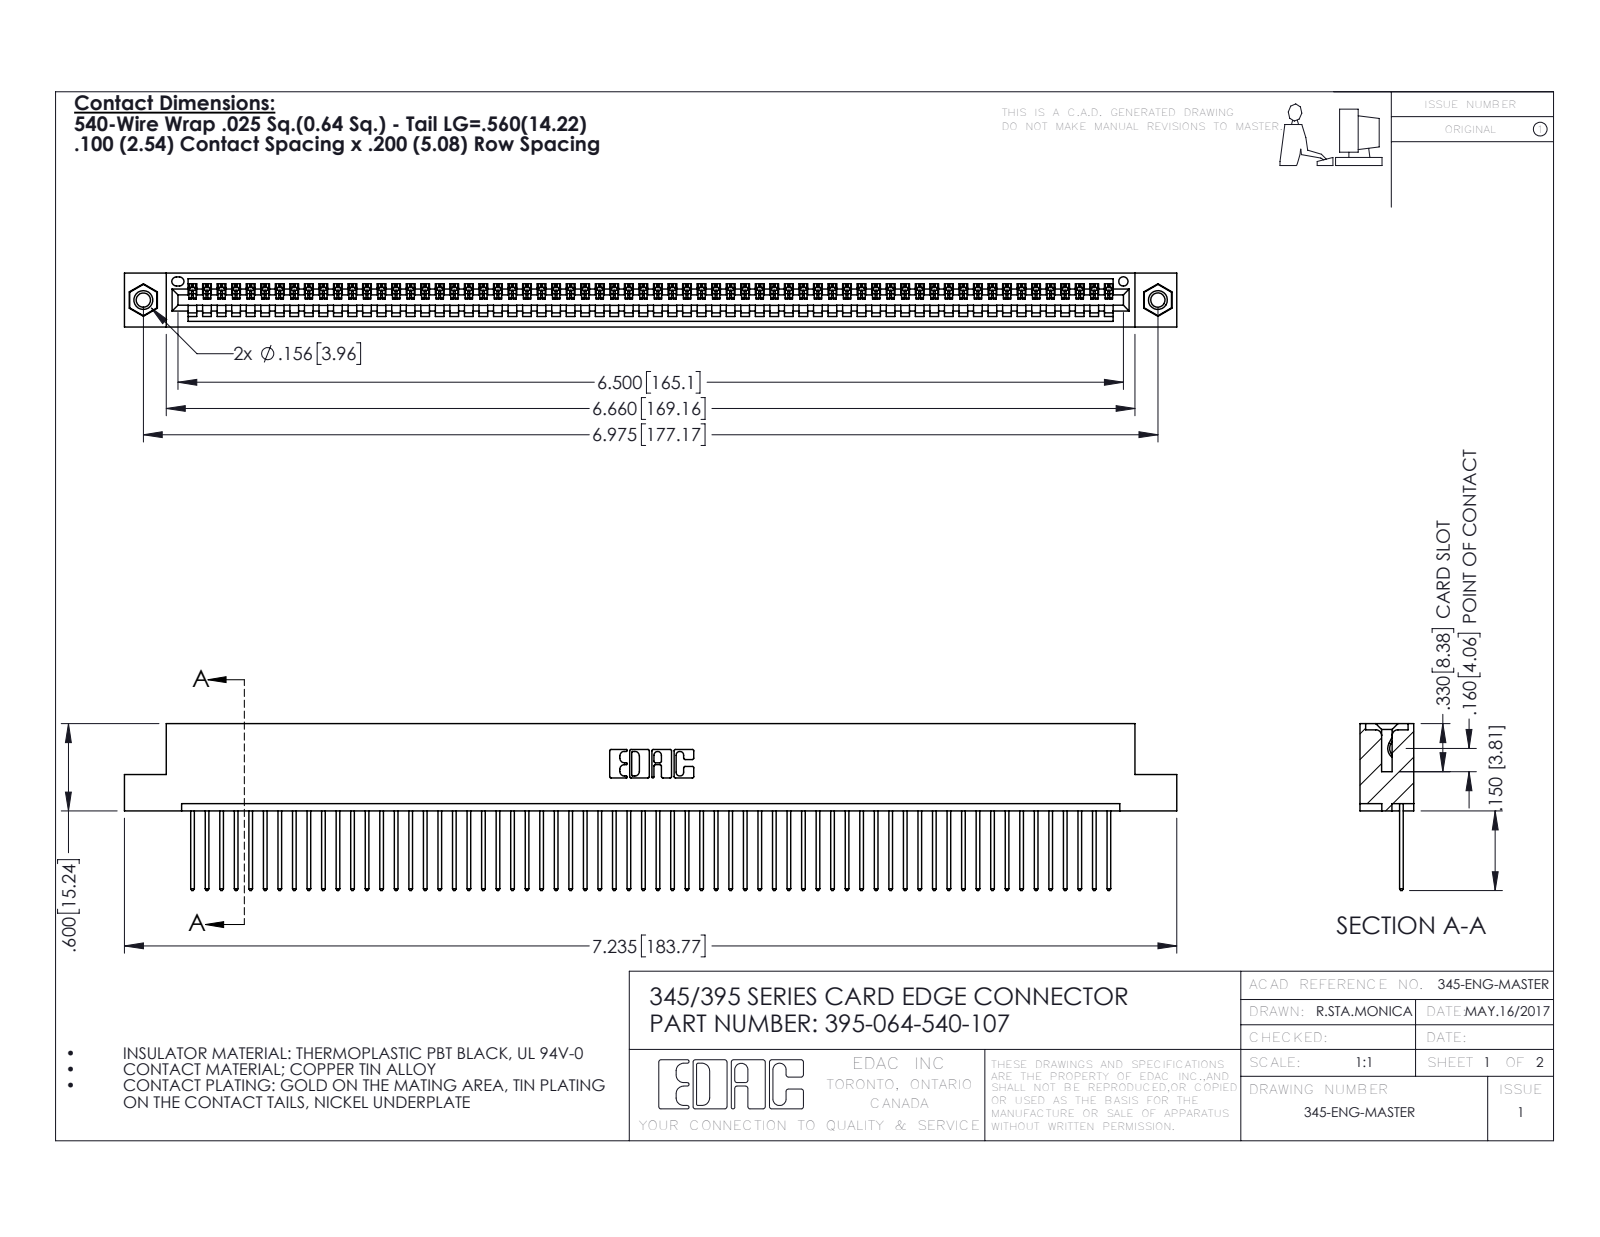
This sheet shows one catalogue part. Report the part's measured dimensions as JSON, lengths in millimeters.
{"part_name": "345-250-001_345-250-005-103; 345 Part_Flush Mounting Lugs - 0.156 Dia-TI; 345-292-001_345-293-140; 395-064-540-107", "step_written_by": "SolidWorks 2016 (CONFIG_CONTROL_DESIGN)", "units": "millimeters", "bodies": {"solids": 67, "faces": 3898, "planar": 2672, "cylindrical": 1210, "other": 16}, "overall_size": [183.8, 29.1, 9.4], "volume_mm3": 17710, "surface_area_mm2": 24490, "round_holes": [[2.5, 2], [3.2, 2], [4, 2], [1.6, 1]], "round_bosses_or_shafts": [[3.9, 2]], "partial_cylinders_radius": [[0.2, 128], [0.3, 128], [0.3, 22], [0.2, 6], [0.8, 6], [0.7, 3], [0.8, 2], [1, 2]], "face_to_face_distances": [1.8, 7.6, 9.4, 2.5, 6.9, 0.6, 5.1, 5.7, 3.8, 1.8], "hole_center_spacings": [6.9, 171.2, 177.2]}
